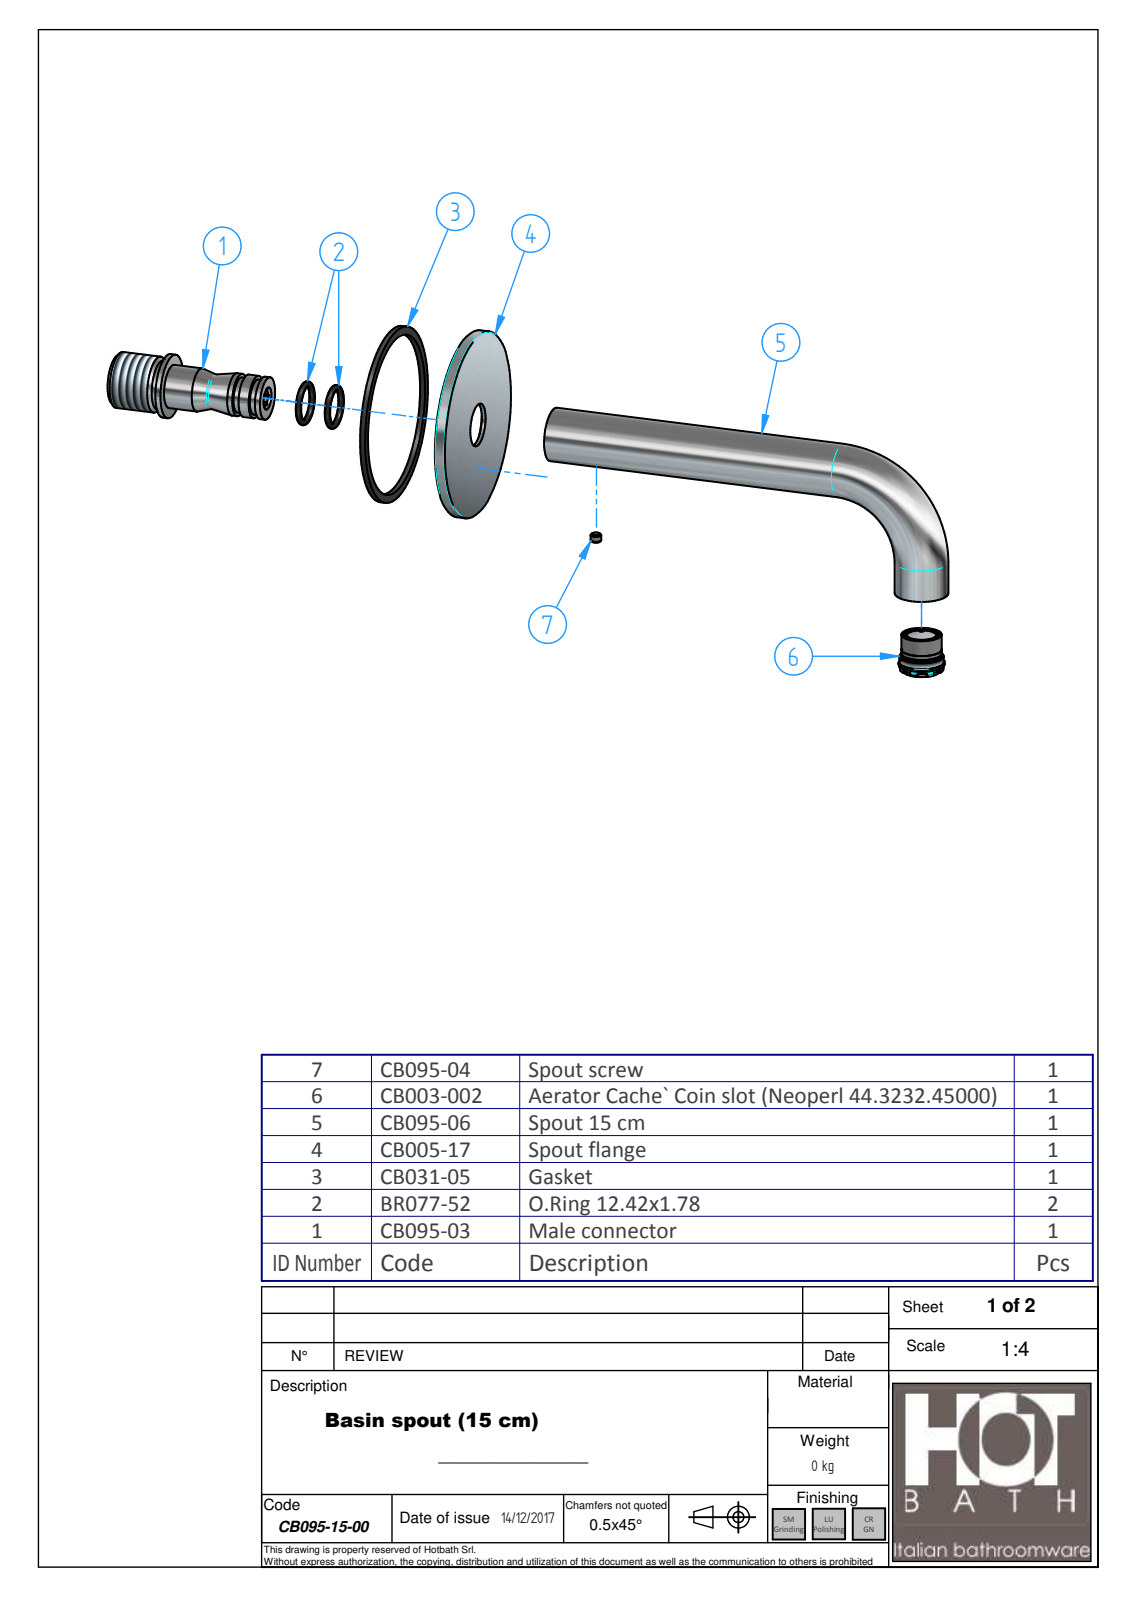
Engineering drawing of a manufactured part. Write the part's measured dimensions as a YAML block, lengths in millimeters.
part_name: "CB095-15-00r1; CB095-06; B077-52; CB031-05 rel1 (+8 more)"
step_written_by: "ST-DEVELOPER v16.7 (AUTOMOTIVE_DESIGN)"
units: millimeters
bodies: {solids: 11, faces: 187, planar: 93, cylindrical: 39, other: 55}
overall_size: [179.5, 81.02, 70]
volume: 44601
surface_area: 39700
round_holes:
  - {diameter: 16, count: 2}
  - {diameter: 3.3, count: 1}
  - {diameter: 6.3, count: 1}
  - {diameter: 11.03, count: 1}
  - {diameter: 12.2, count: 1}
  - {diameter: 13, count: 1}
  - {diameter: 14.58, count: 1}
  - {diameter: 16.1, count: 1}
  - {diameter: 16.3, count: 1}
  - {diameter: 16.75, count: 1}
  - {diameter: 25, count: 1}
  - {diameter: 60, count: 1}
round_bosses_or_shafts:
  - {diameter: 20, count: 2}
  - {diameter: 70, count: 1}
  - {diameter: 66, count: 1}
  - {diameter: 57, count: 1}
  - {diameter: 23.8, count: 1}
  - {diameter: 20.95, count: 1}
  - {diameter: 18.4, count: 1}
  - {diameter: 16.5, count: 1}
face_to_face_distances: [3.2, 0.9, 2.3, 0.8, 2, 1.7, 1.1, 4.3, 2.8, 1.5]
hole_center_spacings: [129]
